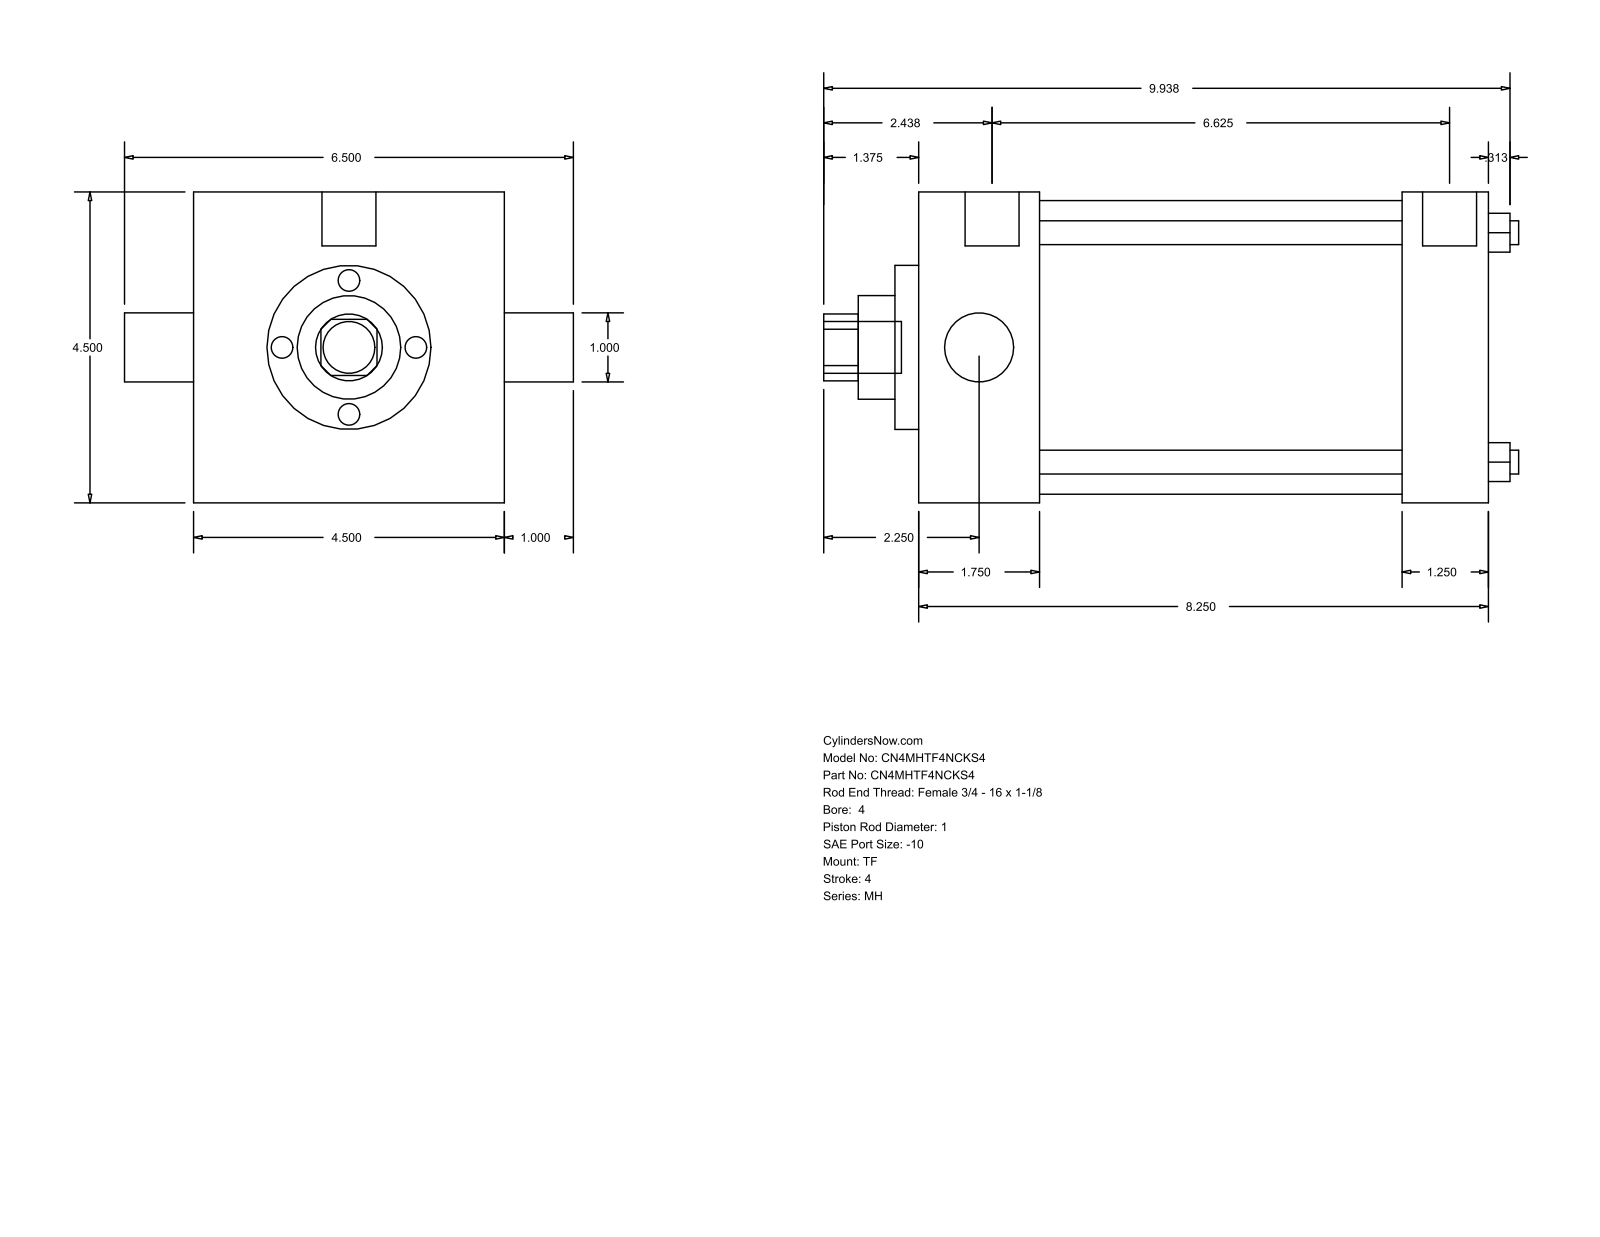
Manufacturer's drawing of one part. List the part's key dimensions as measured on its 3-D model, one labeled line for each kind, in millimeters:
Part name (STEP PRODUCT): MH_TF__0400_1
STEP written by: GSSL Pune (CONFIG_CONTROL_DESIGN)
Units: millimetres
Bodies: 0 solids, 86 faces (61 planar, 25 cylindrical, 0 other)
Overall size (bounding box): 255.59 × 165.1 × 114.3
Round holes (diameter × count): ⌀8.76 ×4, ⌀25.4 ×2, ⌀38.1 ×1, ⌀60.33 ×1, ⌀107.95 ×1
Round bosses / shafts (diameter × count): ⌀8.73 ×3, ⌀19.84 ×2, ⌀19.05 ×1
Partial cylindrical surfaces — rounded edges, fillets, slot ends (radius × count): R12.29 ×1
Main face-to-face distances: 114.3, 209.55, 44.46, 165.09, 177.8, 133.34, 31.75, 8.73, 53.19, 186.53
Hole centre spacings: 59.62, 84.32, 119.25
